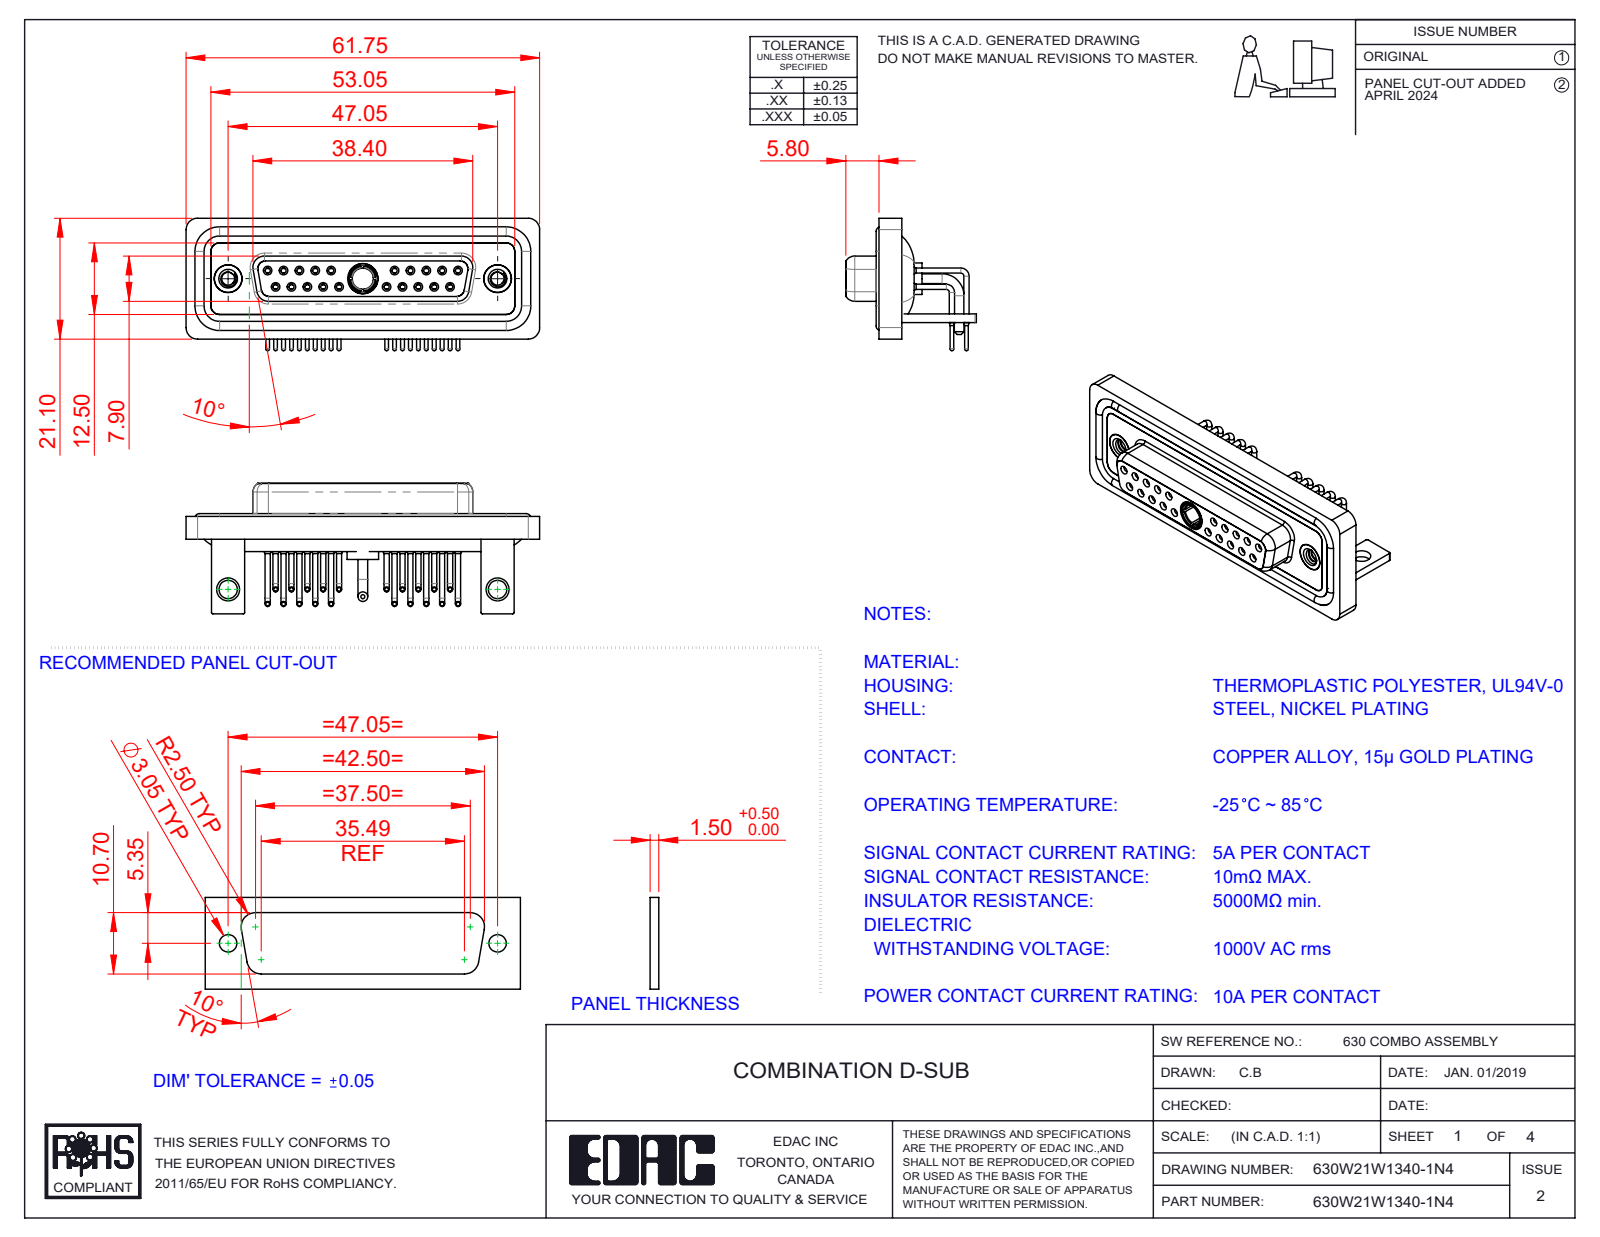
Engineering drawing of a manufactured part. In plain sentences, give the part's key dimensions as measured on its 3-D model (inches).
The part is named "Power Socket_10A RA; 630Combo Housing_21W1; 630Combo Contact Row 2_50 Contacts; 630Combo Waterproof Housing_25 Contacts (+6 more)". Its 3-D file was written by "SolidWorks 2023 (CONFIG_CONTROL_DESIGN)". It is 31 solids with 1572 faces: 454 planar, 697 cylindrical and 421 other. Overall it measures 2.431 by 0.91 by 0.898 inches. Its volume is 0.538 cubic inches and its surface area 23.97 square inches. Round holes: 20 of diameter 0.035, 20 of diameter 0.043, 20 of diameter 0.059, 20 of diameter 0.079, 10 of diameter 0.063, 10 of diameter 0.067, 3 of diameter 0.191, 2 of diameter 0.089, 2 of diameter 0.126, 2 of diameter 0.157, 2 of diameter 0.159, 2 of diameter 0.197. Round bosses or shafts: 20 of diameter 0.035, 20 of diameter 0.026, 14 of diameter 0.063, 2 of diameter 0.195, 2 of diameter 0.189, 2 of diameter 0.067, 1 of diameter 0.217, 1 of diameter 0.205. Partial cylindrical surfaces (rounded edges, fillets, slot ends): 19 of radius 0.079, 18 of radius 0.059, 16 of radius 0.01, 8 of radius 0.053, 8 of radius 0.063, 5 of radius 0.02, 4 of radius 0.024, 4 of radius 0.026. The main face-to-face distances are 0.016, 0.071, 0.114, 0.146, 0.059, 0.161, 0.043, 0.055, 0.063, 0.098. The hole center spacings are 0.124, 0.109, 0.218, 0.327, 0.198, 0.763, 0.826, 0.872.
